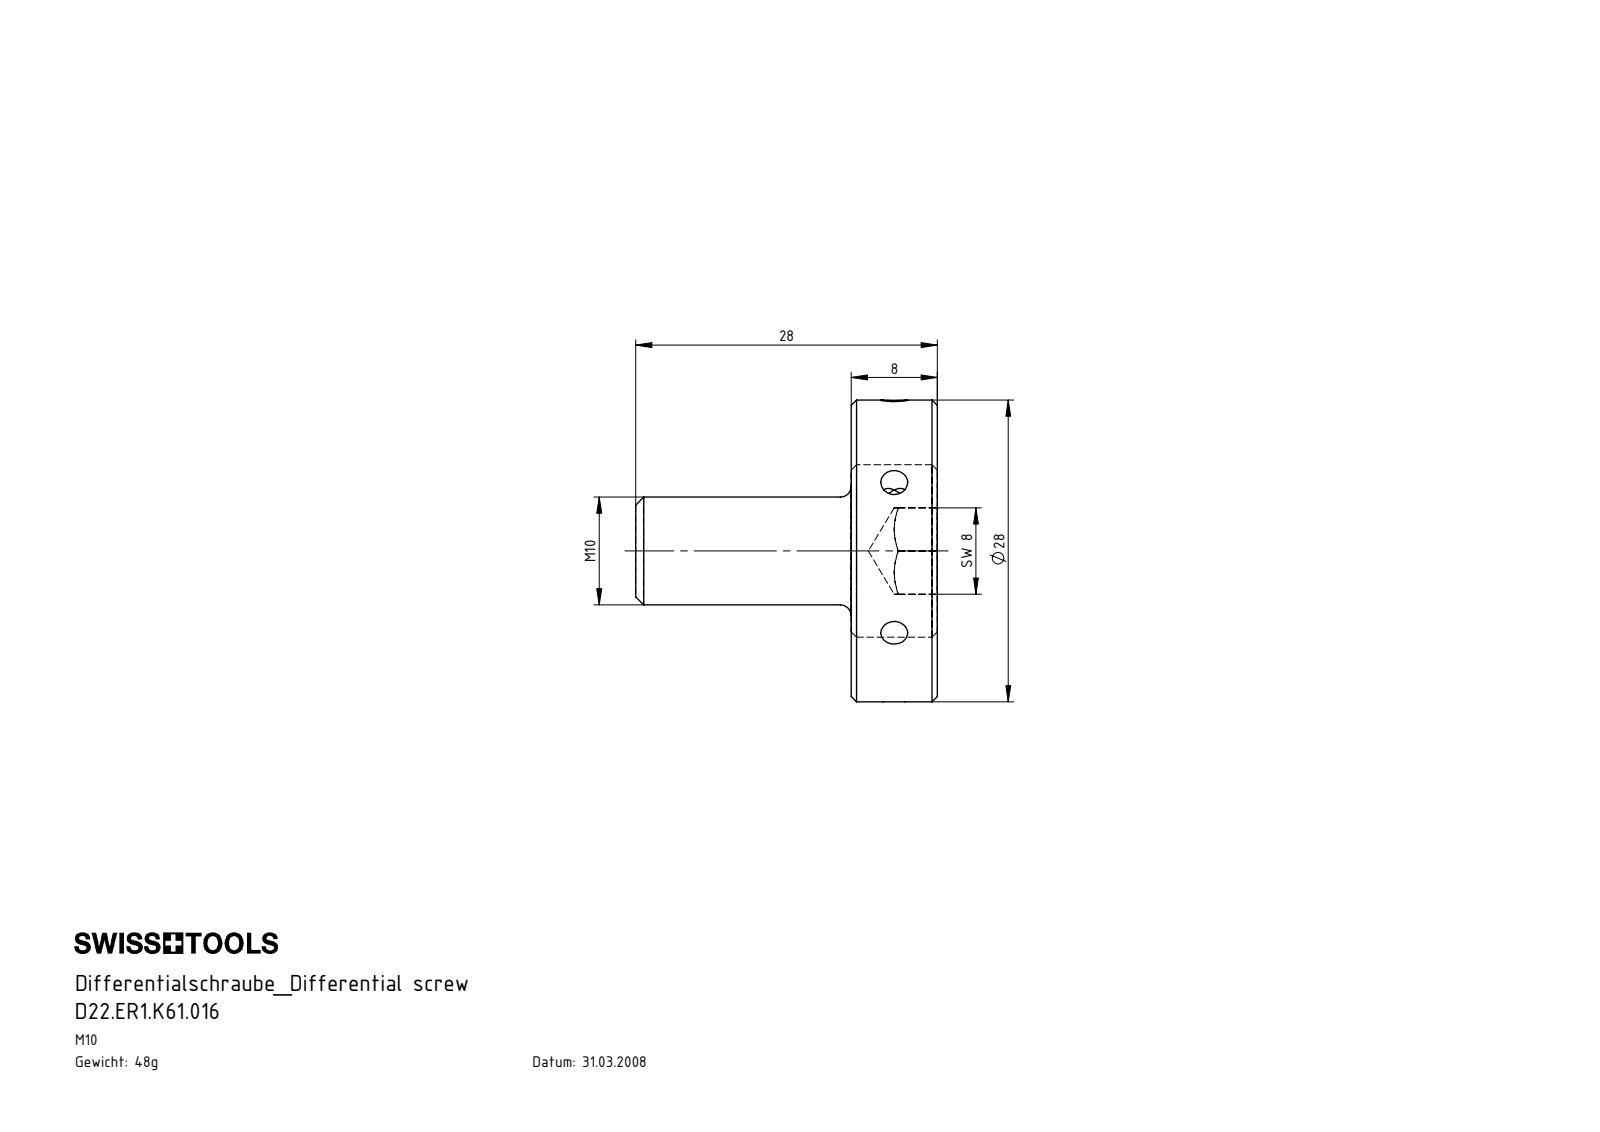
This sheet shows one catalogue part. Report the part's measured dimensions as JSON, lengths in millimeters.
{"part_name": "D22-ER1.K61.016; D22-ER1.K62.008_A; D22-ER1.K63.016_A", "step_written_by": "SolidWorks 2012 (AUTOMOTIVE_DESIGN)", "units": "millimeters", "bodies": {"solids": 2, "faces": 145, "planar": 11, "cylindrical": 78, "other": 56}, "overall_size": [28, 28, 28], "volume_mm3": 6136, "surface_area_mm2": 3705, "round_holes": [[2.5, 12], [15, 1]], "round_bosses_or_shafts": [[28, 1], [16, 1], [10, 1]], "face_to_face_distances": [8, 20, 28], "hole_center_spacings": [10, 17.31, 17.32, 17.33, 19.99, 20, 20.01]}
